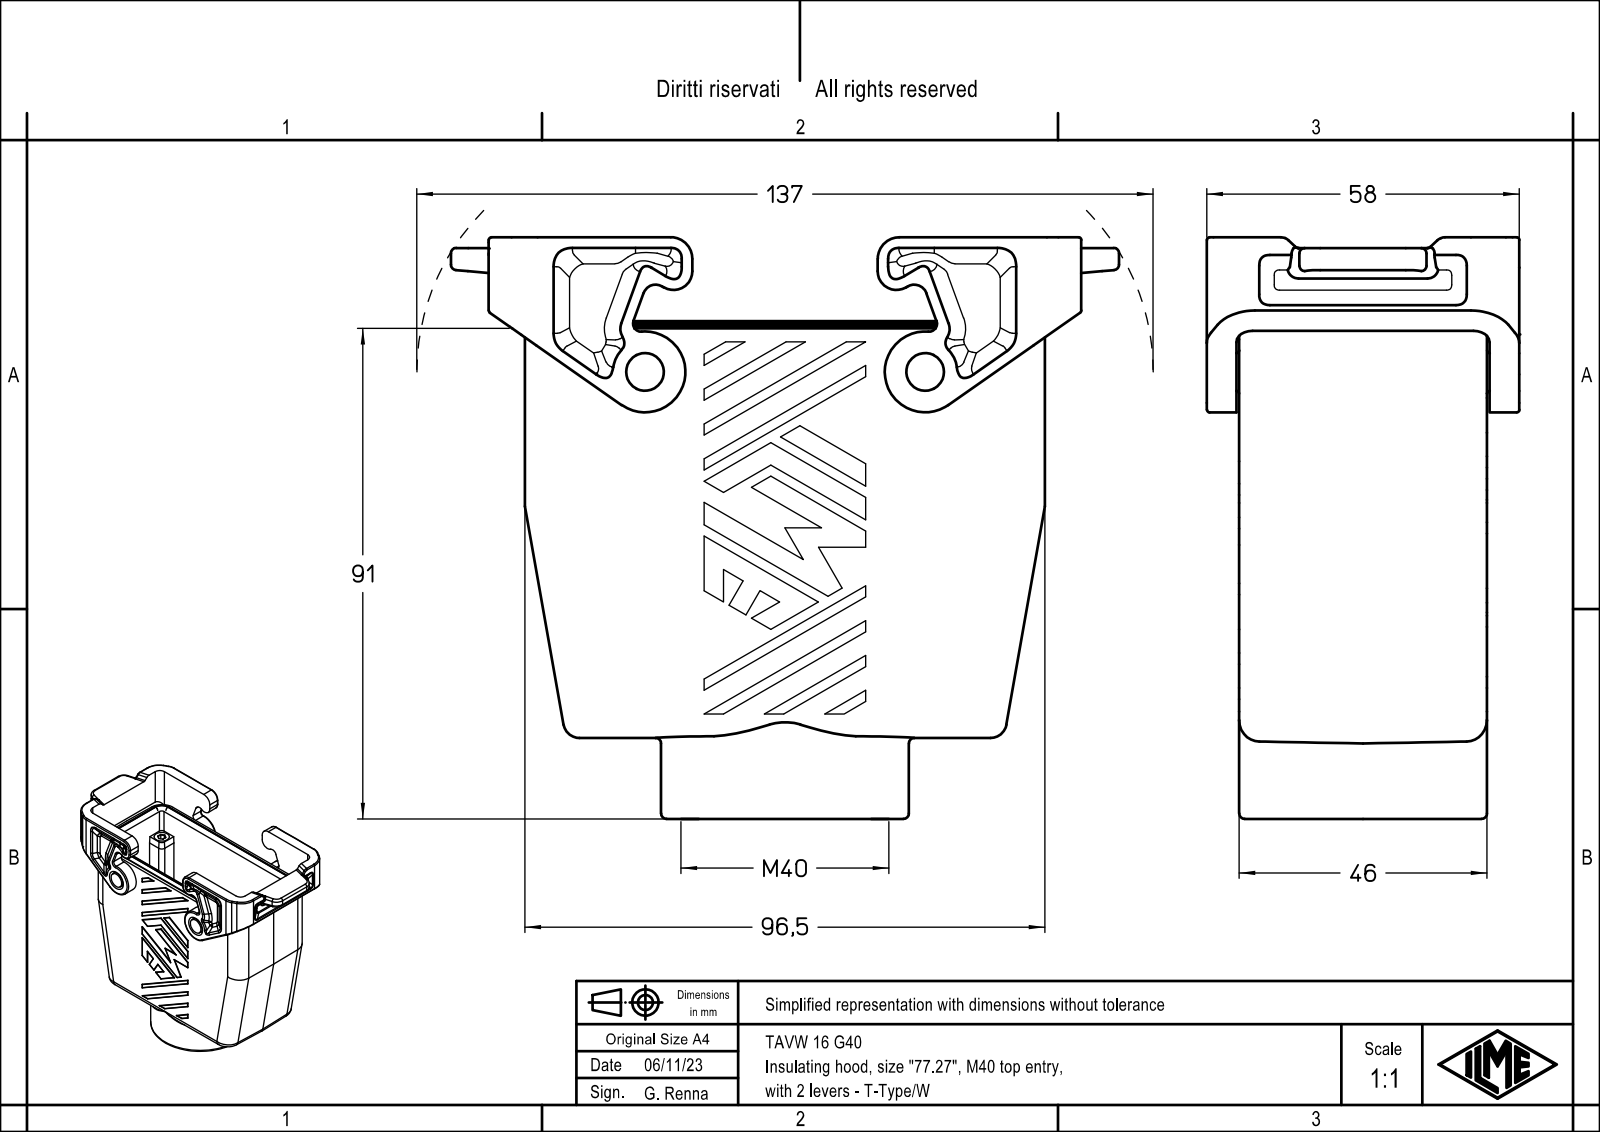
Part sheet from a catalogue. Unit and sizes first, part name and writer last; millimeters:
Units: millimetres
Overall size (bounding box): 124 × 107.9 × 58
Round holes (diameter × count): ⌀34 ×1, ⌀38.6 ×1
Round bosses / shafts (diameter × count): ⌀7 ×2, ⌀46 ×1
Partial cylindrical surfaces — rounded edges, fillets, slot ends (radius × count): R0.15 ×88, R3 ×20, R1 ×16, R2 ×16, R1.5 ×10, R1.3 ×8, R6 ×8, R7 ×8
Main face-to-face distances: 5.4, 40.6, 35.2, 46, 0.5, 5.9, 41.1, 46.5, 5.5, 6
Volume: 152 952 mm³ · Surface area: 60 673 mm²
Bodies: 1 solid, 562 faces (218 planar, 282 cylindrical, 62 other)
Part name (STEP PRODUCT): TAVW 16 G40
STEP written by: Creo Elements/Direct Modeling 20.1B 02-Apr-2019 (C) Parametric Technology GmbH (AUTOMOTIVE_DESIGN)
